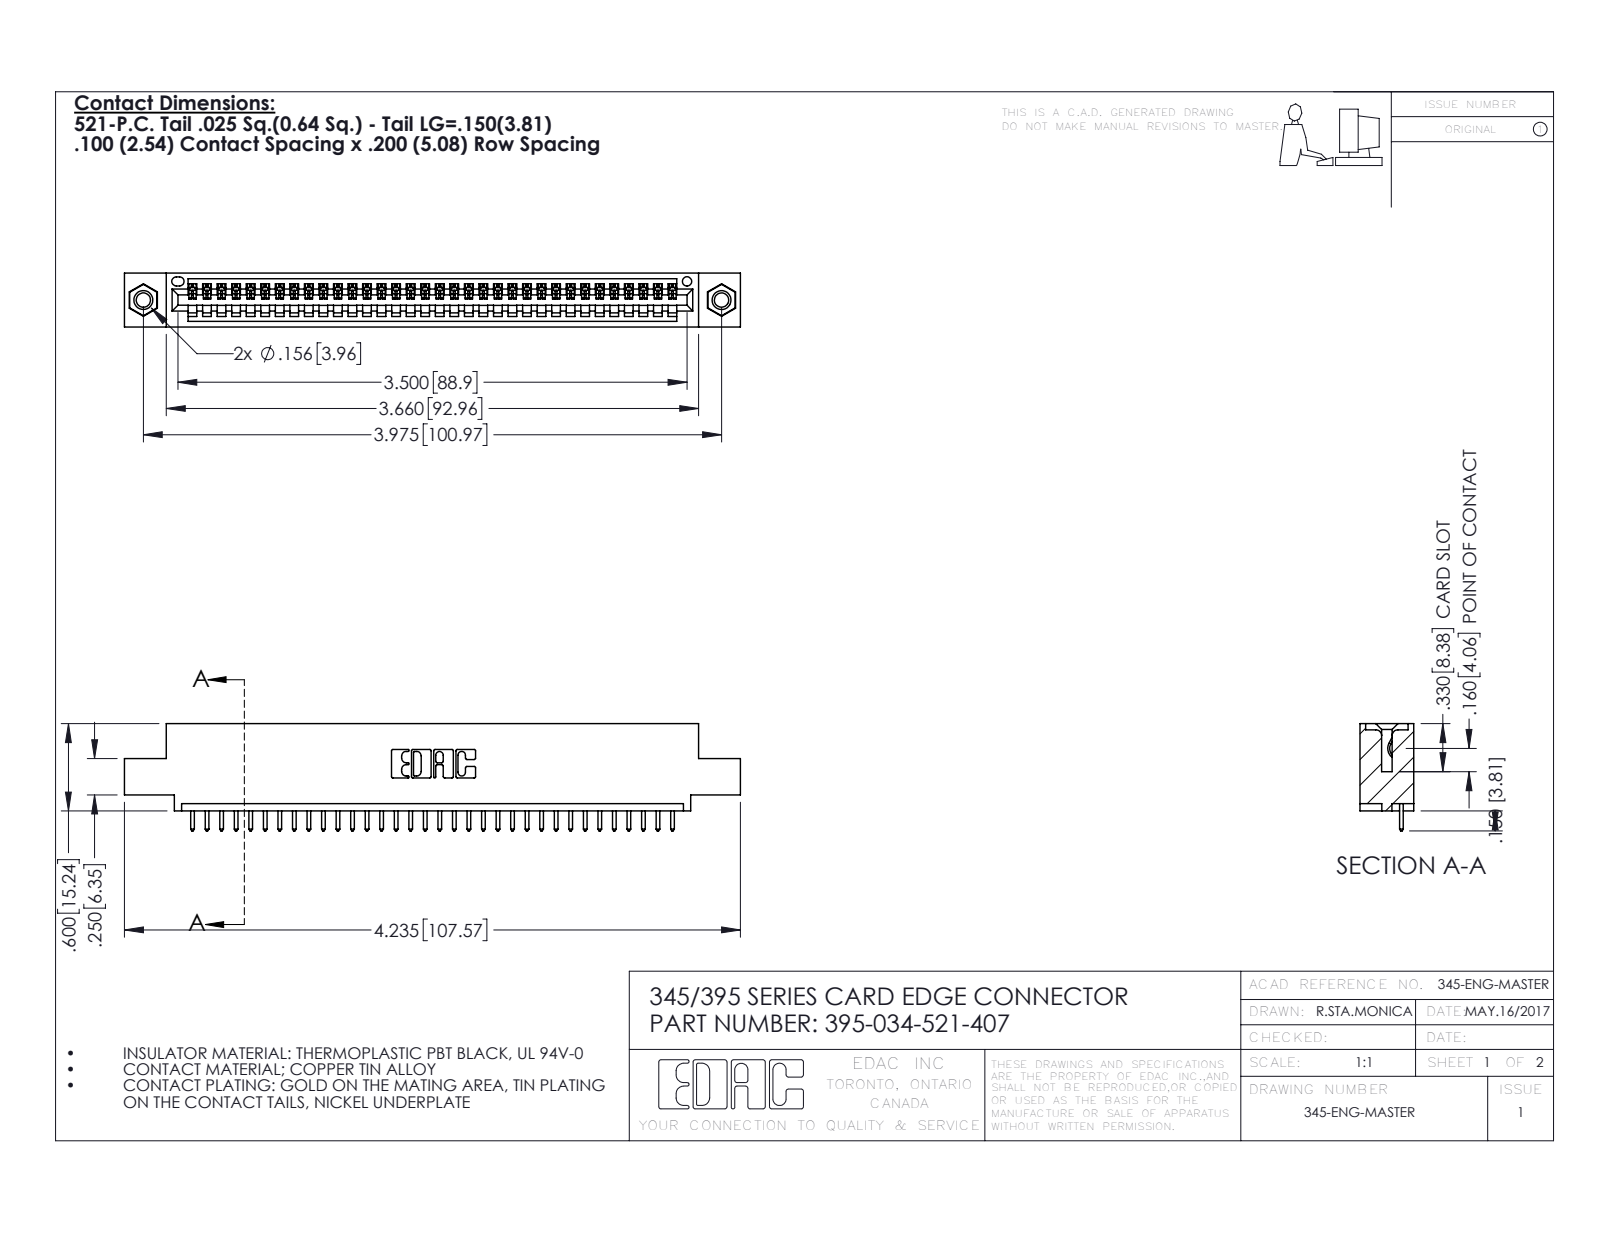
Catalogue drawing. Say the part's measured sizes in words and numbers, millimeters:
The part is named "345-250-001_345-250-005-103; 345-292-001_345-293-121; 395-034-521-407; 345 Part_0.110 Offset - 0.156 Dia-TI". Its 3-D file was written by "SolidWorks 2016 (CONFIG_CONTROL_DESIGN)". It is 37 solids with 2162 faces: 1476 planar, 670 cylindrical and 16 other. Overall it measures 107.6 by 18.7 by 9.4 millimeters. Its volume is 9 960 cubic millimeters and its surface area 12 870 square millimeters. Round holes: 2 of diameter 2.5, 2 of diameter 3.2, 2 of diameter 4, 1 of diameter 1.6. Round bosses or shafts: 2 of diameter 3.9. Partial cylindrical surfaces (rounded edges, fillets, slot ends): 68 of radius 0.2, 68 of radius 0.3, 22 of radius 0.3, 6 of radius 0.2, 6 of radius 0.8, 3 of radius 0.7, 2 of radius 0.8, 2 of radius 1. The main face-to-face distances are 1.8, 7.6, 9.4, 5.1, 2.5, 6.9, 0.6, 5.7, 3.8, 1.8. The hole center spacings are 6.9, 95, 101.
